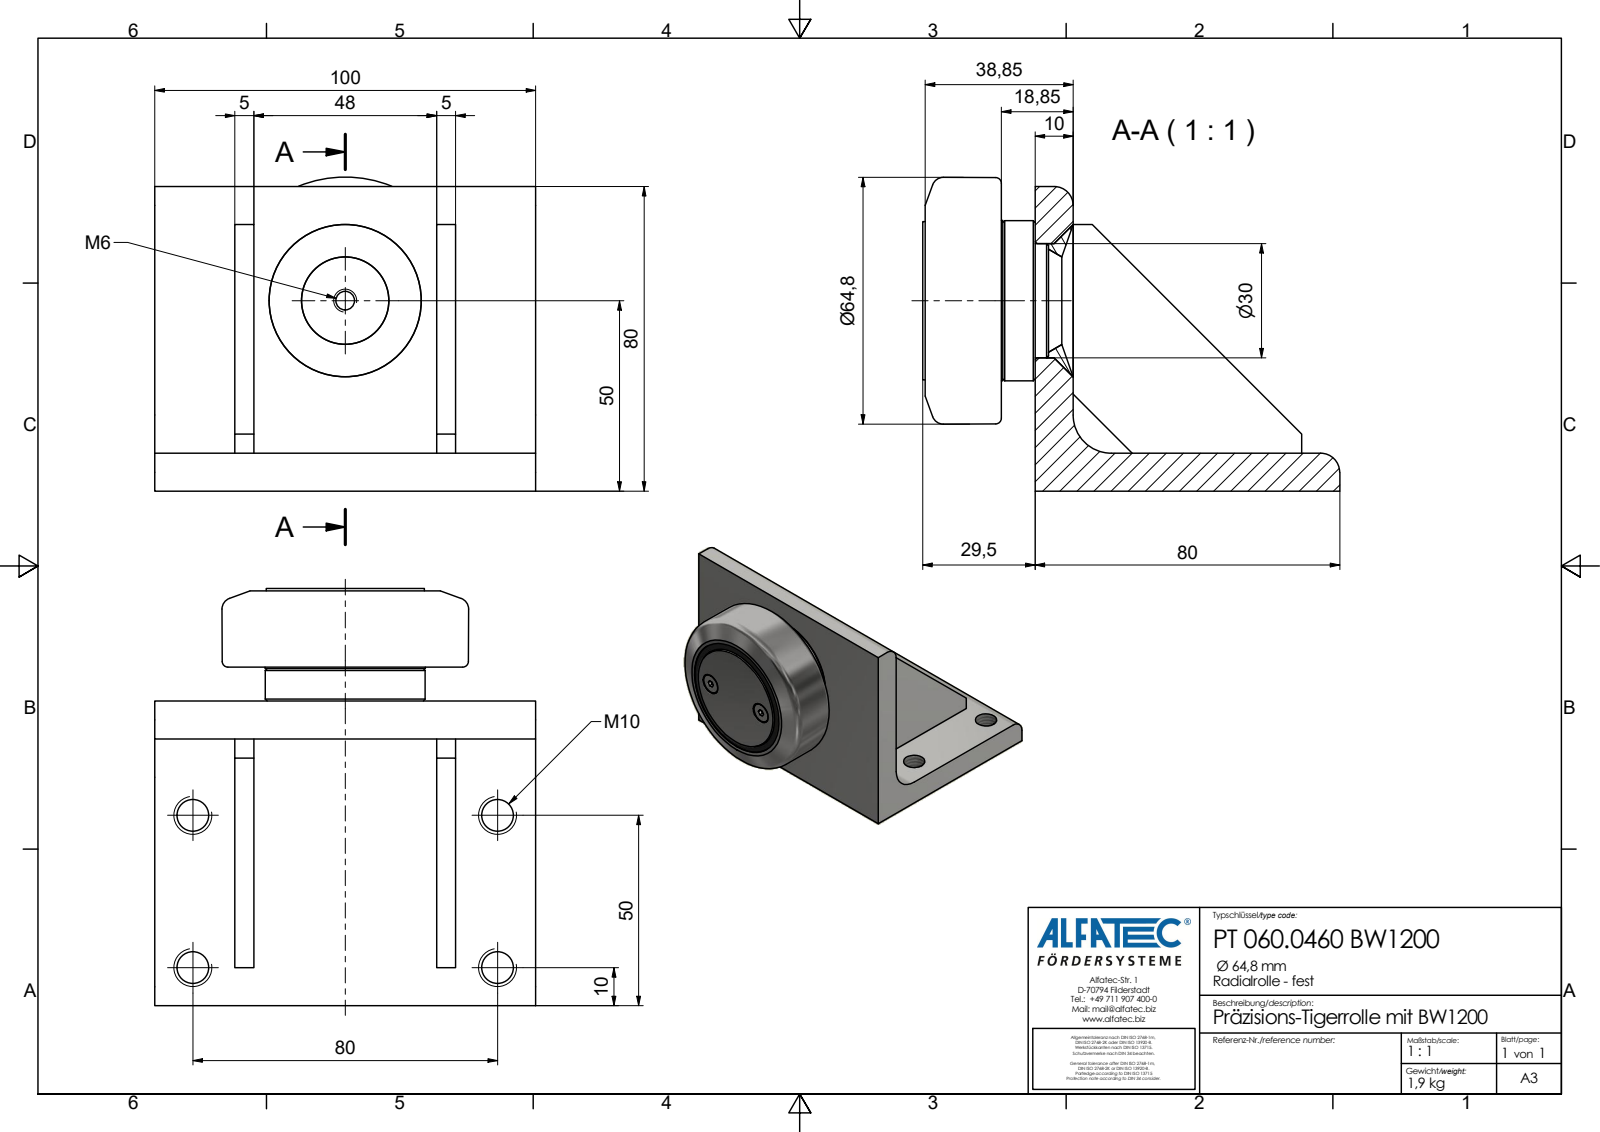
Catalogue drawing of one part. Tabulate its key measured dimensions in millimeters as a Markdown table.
| quantity | value |
| --- | --- |
| part name | PT 060.0460 BW1200_Kontur |
| STEP written by | Autodesk Inventor 2020 (AP242_MANAGED_MODEL_BASED_3D_ENGINEERING_MIM_LF) |
| units | millimeters |
| bodies | 1 solid, 313 faces (195 planar, 104 cylindrical, 14 other) |
| overall size | 109.5 × 100 × 82.4 |
| volume | 239 986 mm³ |
| surface area | 65 138 mm² |
| round holes (diameter × count) | 8.38 × 4, 3 × 2, 8.3 × 2, 4.92 × 1, 38 × 1, 42 × 1, 42.97 × 1, 47 × 1, 50 × 1 |
| round bosses / shafts (diameter × count) | 4 × 36, 7.8 × 2, 45.5 × 1, 45 × 1, 42.1 × 1, 41.5 × 1, 37 × 1 |
| partial cylindrical surfaces (radius × count) | 5 × 2, 10 × 1 |
| main face-to-face distances | 10, 5, 53, 21, 26, 74, 79, 58, 48, 8.85 |
| hole center spacings | 14, 40, 62.1, 62.48, 80, 89.44, 96.21, 96.66 |
